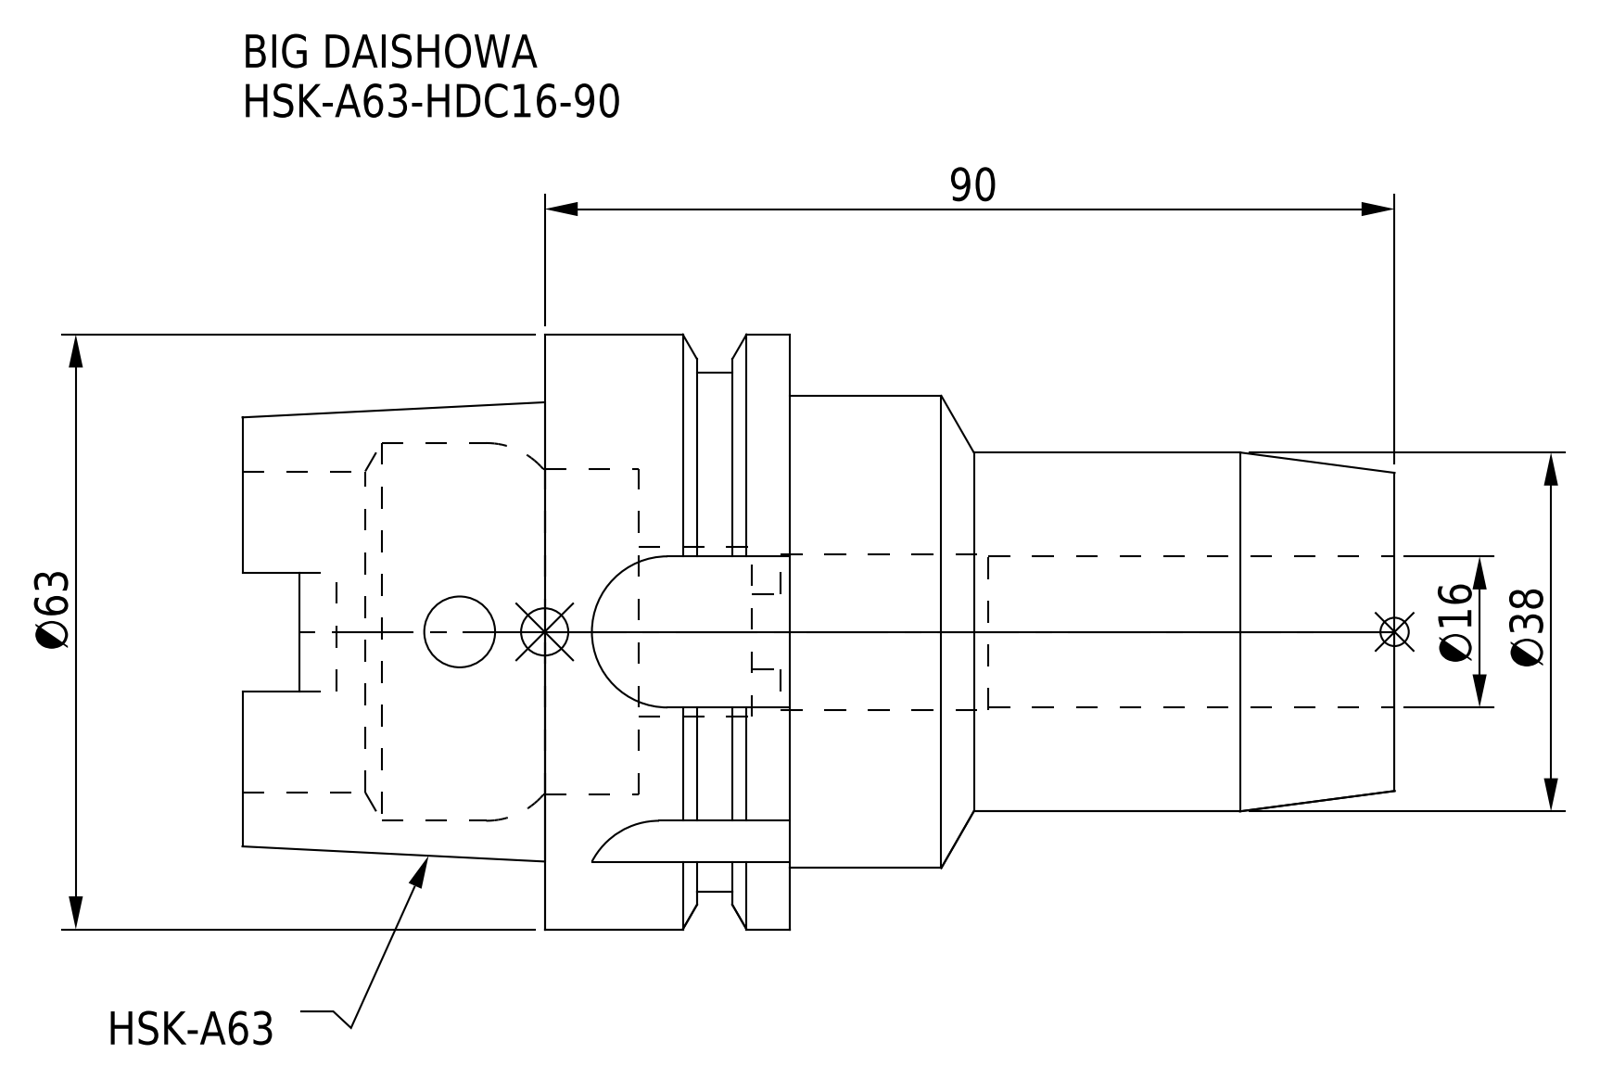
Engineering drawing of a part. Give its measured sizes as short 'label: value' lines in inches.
name: HSK-A63-HDC16-90
written by: CREO PARAMETRIC BY PTC INC, 2016380 (AUTOMOTIVE_DESIGN)
unit: in
bodies: 1 solid, 95 faces (38 planar, 39 cylindrical, 18 other)
size: 4.803 × 2.48 × 2.48
volume: 9.368 in³; area: 51.53 in²
holes: 1× ⌀0.295, 1× ⌀0.315, 1× ⌀0.63, 1× ⌀0.65, 1× ⌀0.709, 1× ⌀1.339, 1× ⌀1.358, 1× ⌀1.575
bosses: 1× ⌀2.48, 1× ⌀2.165, 1× ⌀1.969, 1× ⌀1.496
rounds: 4× R0.113, 4× R0.315
face distances: 1.024, 2.52, 3.543, 3.152, 0.632, 0.392, 4.803, 2.283, 1.652, 1.26
